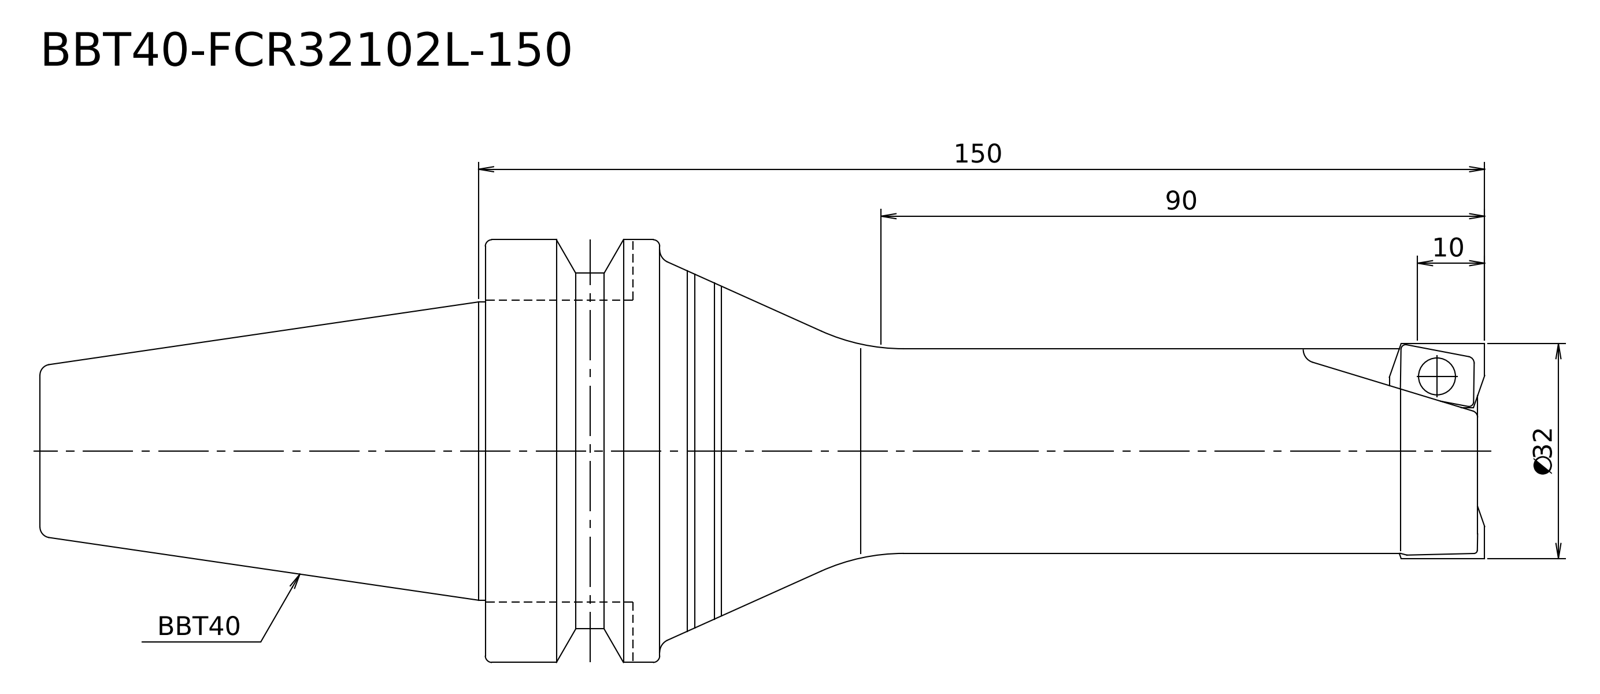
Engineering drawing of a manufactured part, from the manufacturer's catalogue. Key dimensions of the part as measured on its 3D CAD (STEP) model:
STEP written by: Kubotek KeyCreator V8.5.1 (14335) (CONFIG_CONTROL_DESIGN)
Units: millimetres
Bodies: 1 solid, 17 faces (4 planar, 6 cylindrical, 7 other)
Overall size (bounding box): 215.4 × 63 × 63
Volume: 256 888 mm³ · Surface area: 30 232 mm²
Round bosses / shafts (diameter × count): ⌀63 ×1, ⌀53 ×1, ⌀44.45 ×1, ⌀32 ×1, ⌀30.5 ×1
Main face-to-face distances: 149, 215.4, 66.4, 123, 26, 92.4
